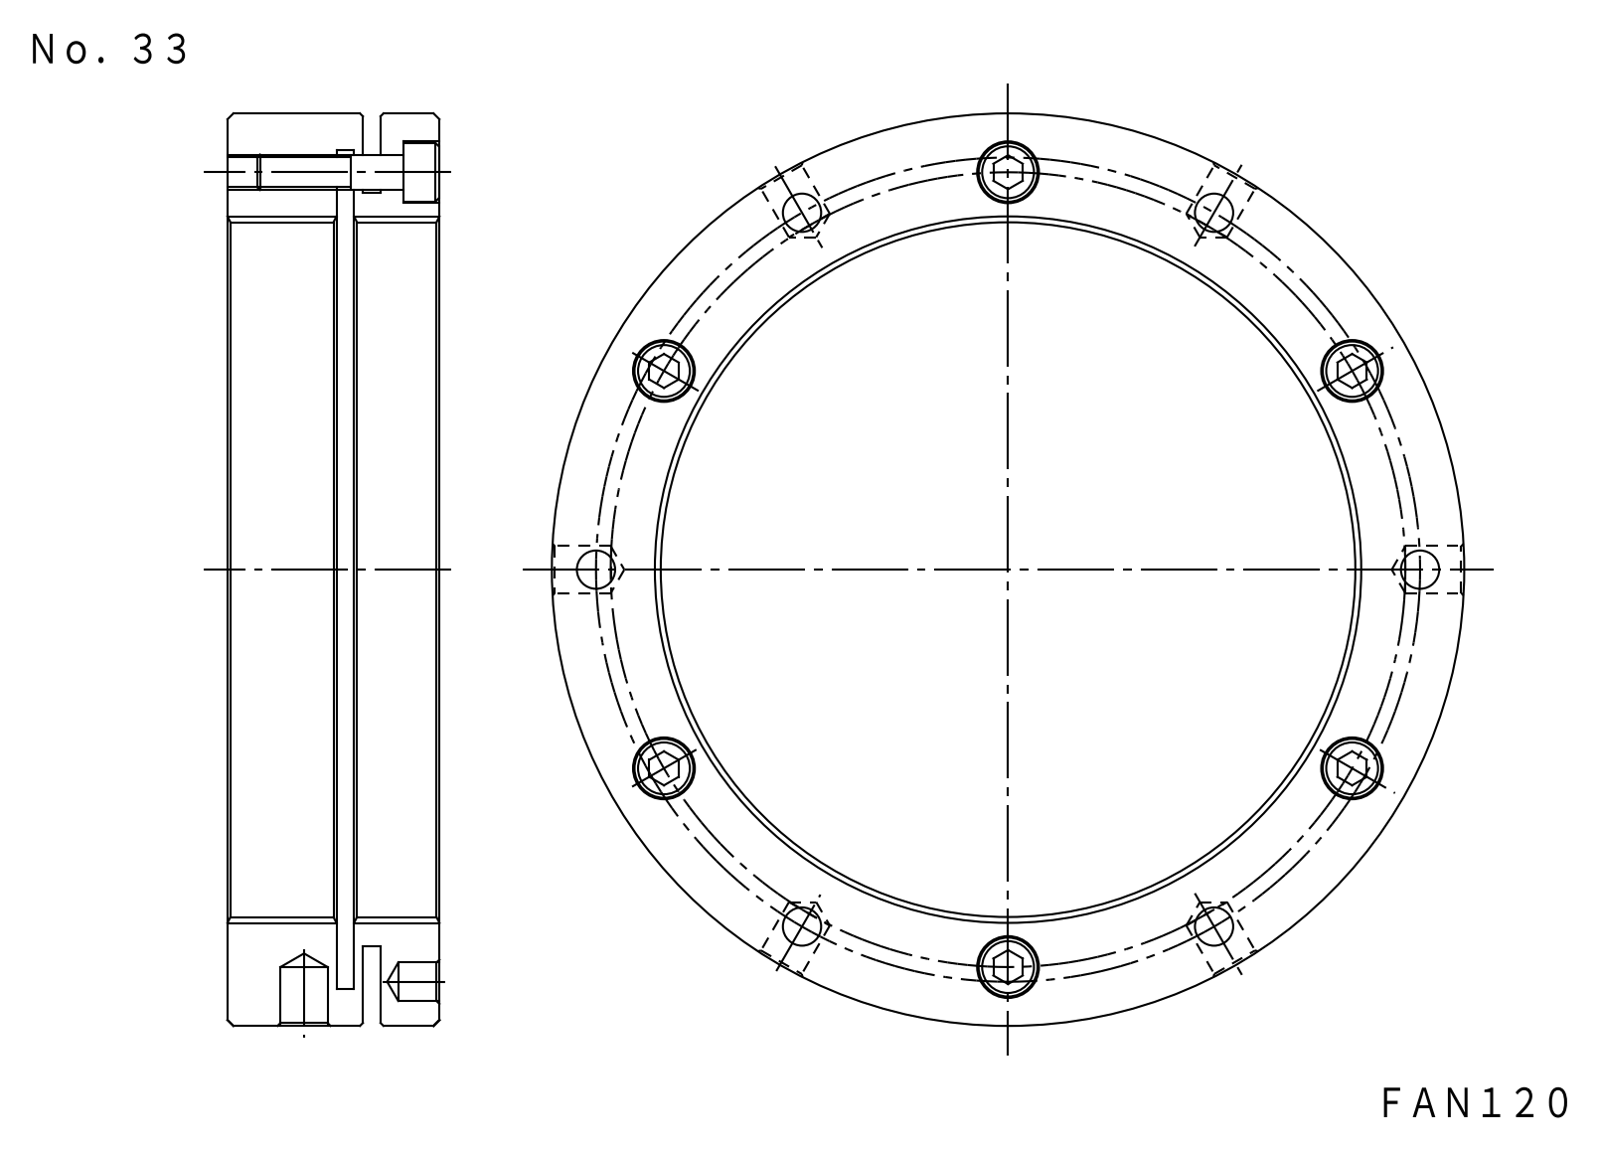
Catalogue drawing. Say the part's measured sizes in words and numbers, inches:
The part is named "FKD FAN120; M6X25_default". Its 3-D file was written by "SolidWorks 2012 (CONFIG_CONTROL_DESIGN)". It is 7 solids with 204 faces: 72 planar, 108 cylindrical and 24 other. Overall it measures 6.102 by 6.102 by 1.417 inches. Its volume is 14.4 cubic inches and its surface area 120 square inches. Round holes: 6 of diameter 0.194, 6 of diameter 0.248, 6 of diameter 0.268, 6 of diameter 0.433, 3 of diameter 0.315, 1 of diameter 4.724, 1 of diameter 5.709. Round bosses or shafts: 6 of diameter 0.394, 6 of diameter 0.236, 1 of diameter 6.102, 1 of diameter 5.157. The main face-to-face distances are 0.118, 0.177, 1.417, 0.965, 0.453, 1.083, 0.335, 0.787, 0.295, 0.63. The hole center spacings are 1.417, 2.717, 2.756, 3.87, 5.286, 4.773, 4.705, 5.286.
